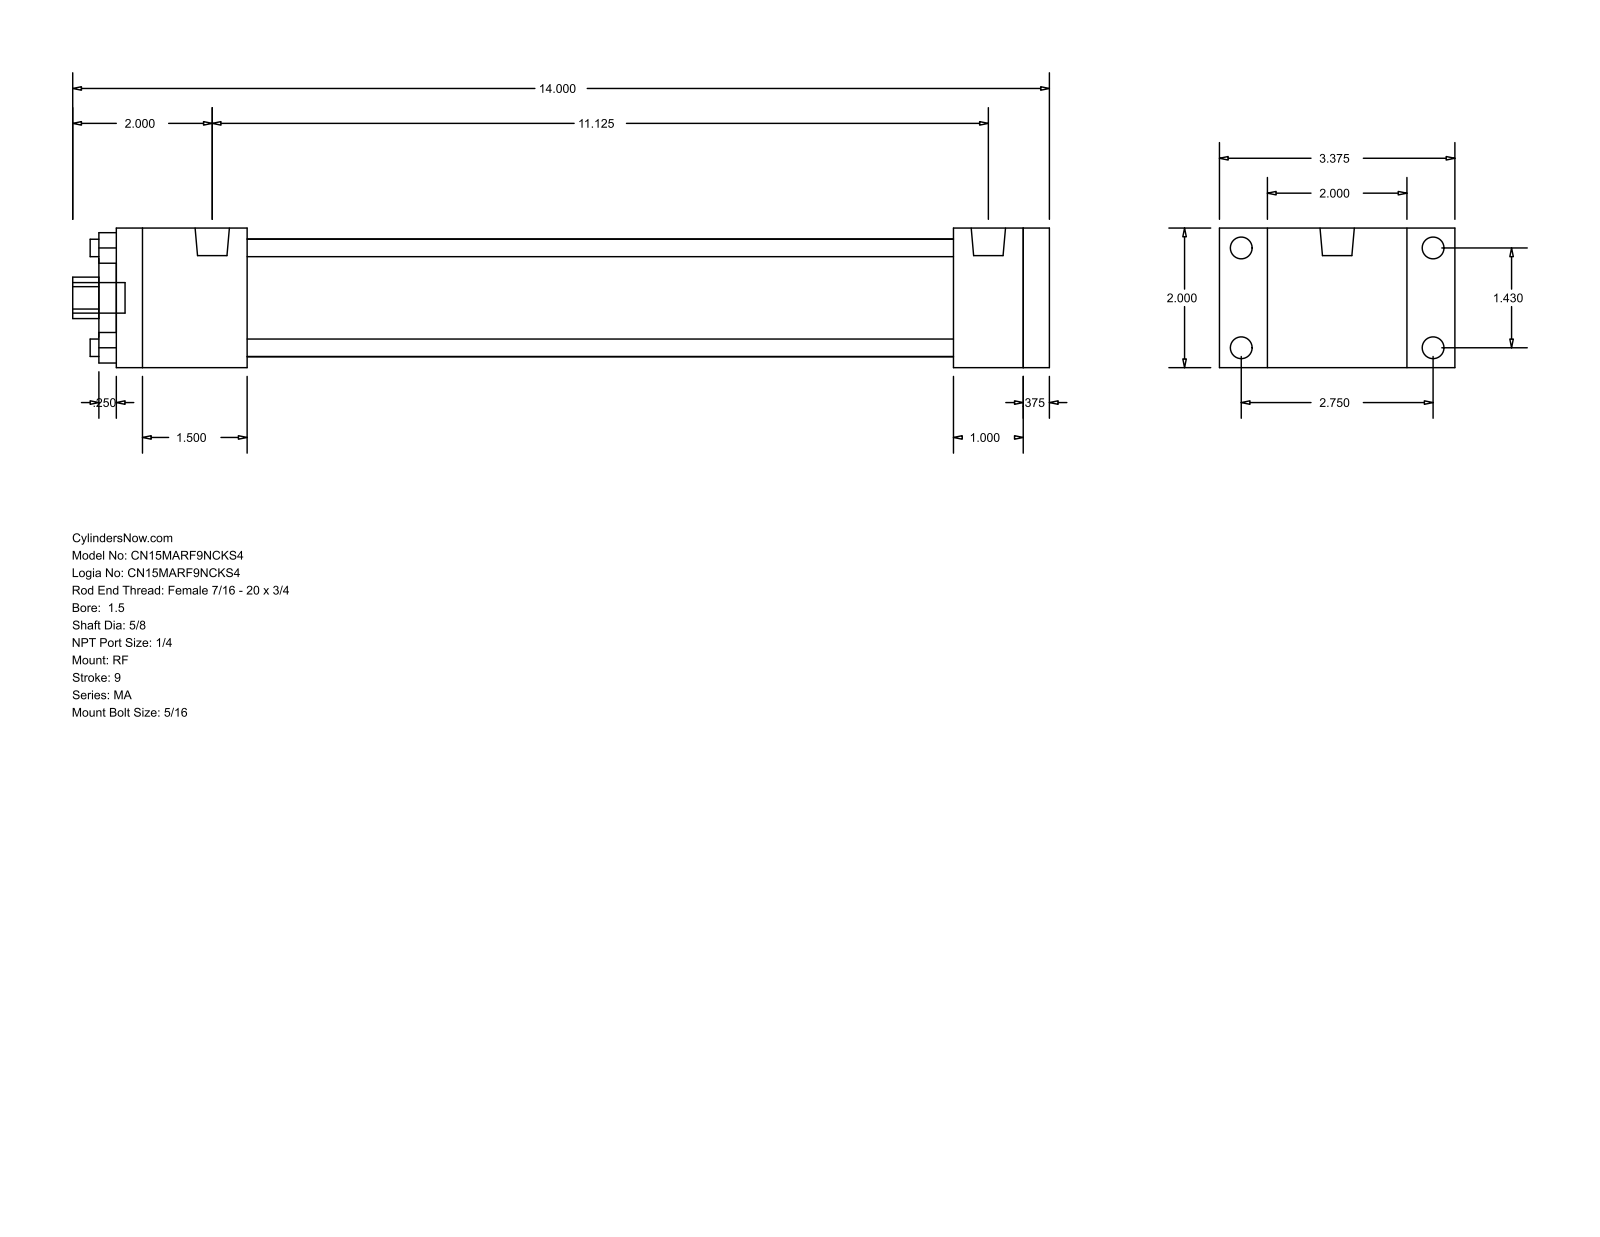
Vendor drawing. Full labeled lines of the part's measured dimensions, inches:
Part name (STEP PRODUCT): MA_RF__0150_0.625
STEP written by: GSSL Pune (CONFIG_CONTROL_DESIGN)
Units: inches
Bodies: 0 solids, 92 faces (64 planar, 28 cylindrical, 0 other)
Overall size (bounding box): 14 × 3.375 × 2
Round holes (diameter × count): ⌀0.25 ×4, ⌀0.625 ×1, ⌀1.125 ×1, ⌀1.69 ×1
Round bosses / shafts (diameter × count): ⌀0.313 ×8, ⌀0.492 ×2, ⌀0.437 ×1
Partial cylindrical surfaces — rounded edges, fillets, slot ends (radius × count): R0.297 ×1
Main face-to-face distances: 2, 0.375, 13.375, 13, 12, 1, 1.375, 1.875, 10.125, 11.125
Hole centre spacings: 1.011, 1.43, 2.022
